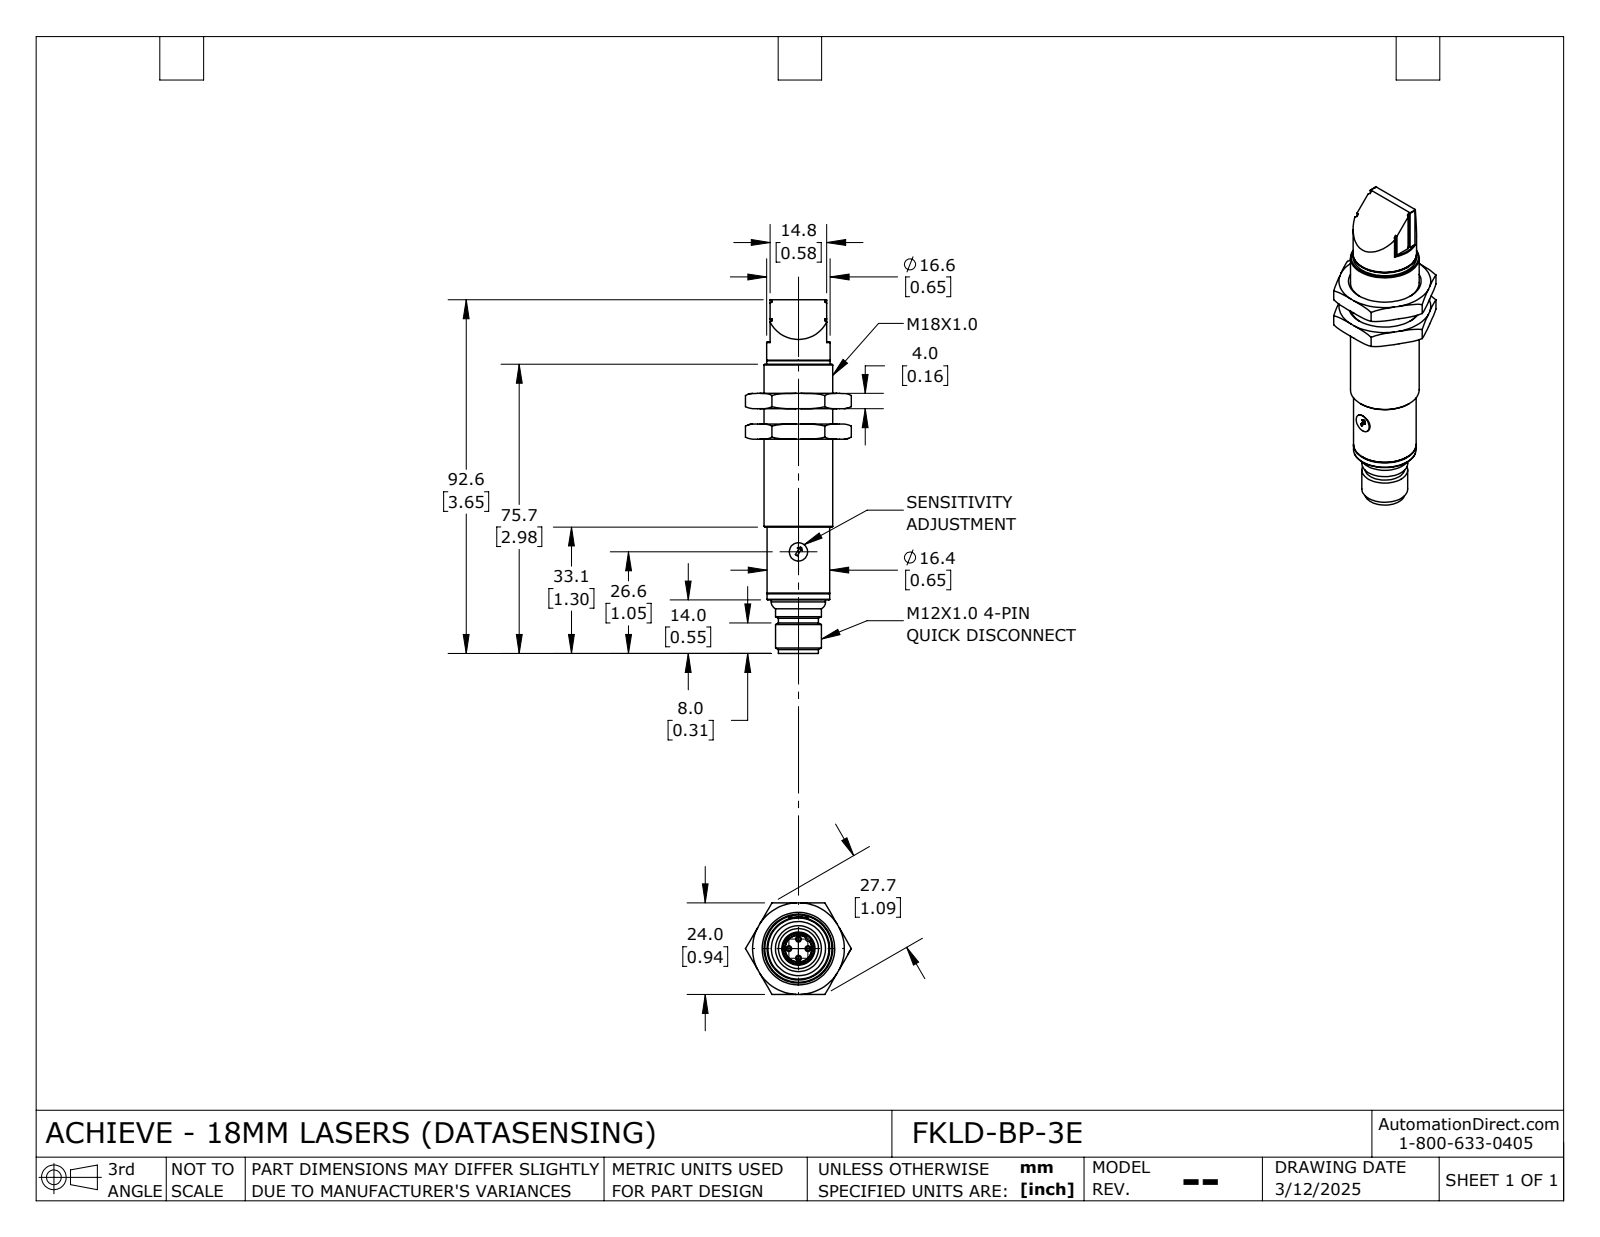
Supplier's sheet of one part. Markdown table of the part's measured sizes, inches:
| quantity | value |
| --- | --- |
| part name | FKLD-BP-3E_Default |
| STEP written by | SolidWorks 2024 (CONFIG_CONTROL_DESIGN) |
| units | inches |
| bodies | 3 solids, 156 faces (73 planar, 31 cylindrical, 52 other) |
| overall size | 3.646 × 1.091 × 0.945 |
| volume | 1.243 in³ |
| surface area | 12.62 in² |
| round holes (diameter × count) | 0.278 × 1, 0.327 × 1, 0.583 × 1, 0.709 × 1 |
| round bosses / shafts (diameter × count) | 0.039 × 4, 0.654 × 1, 0.646 × 1, 0.559 × 1, 0.472 × 1, 0.413 × 1, 0.276 × 1, 0.189 × 1 |
| partial cylindrical surfaces (radius × count) | 0.004 × 2, 0.02 × 2, 0.297 × 2, 0.024 × 1, 0.053 × 1 |
| main face-to-face distances | 0.157, 0.315, 0.945, 0.473, 0.481, 0.788, 0.796, 0.631, 0.639, 0.472 |
